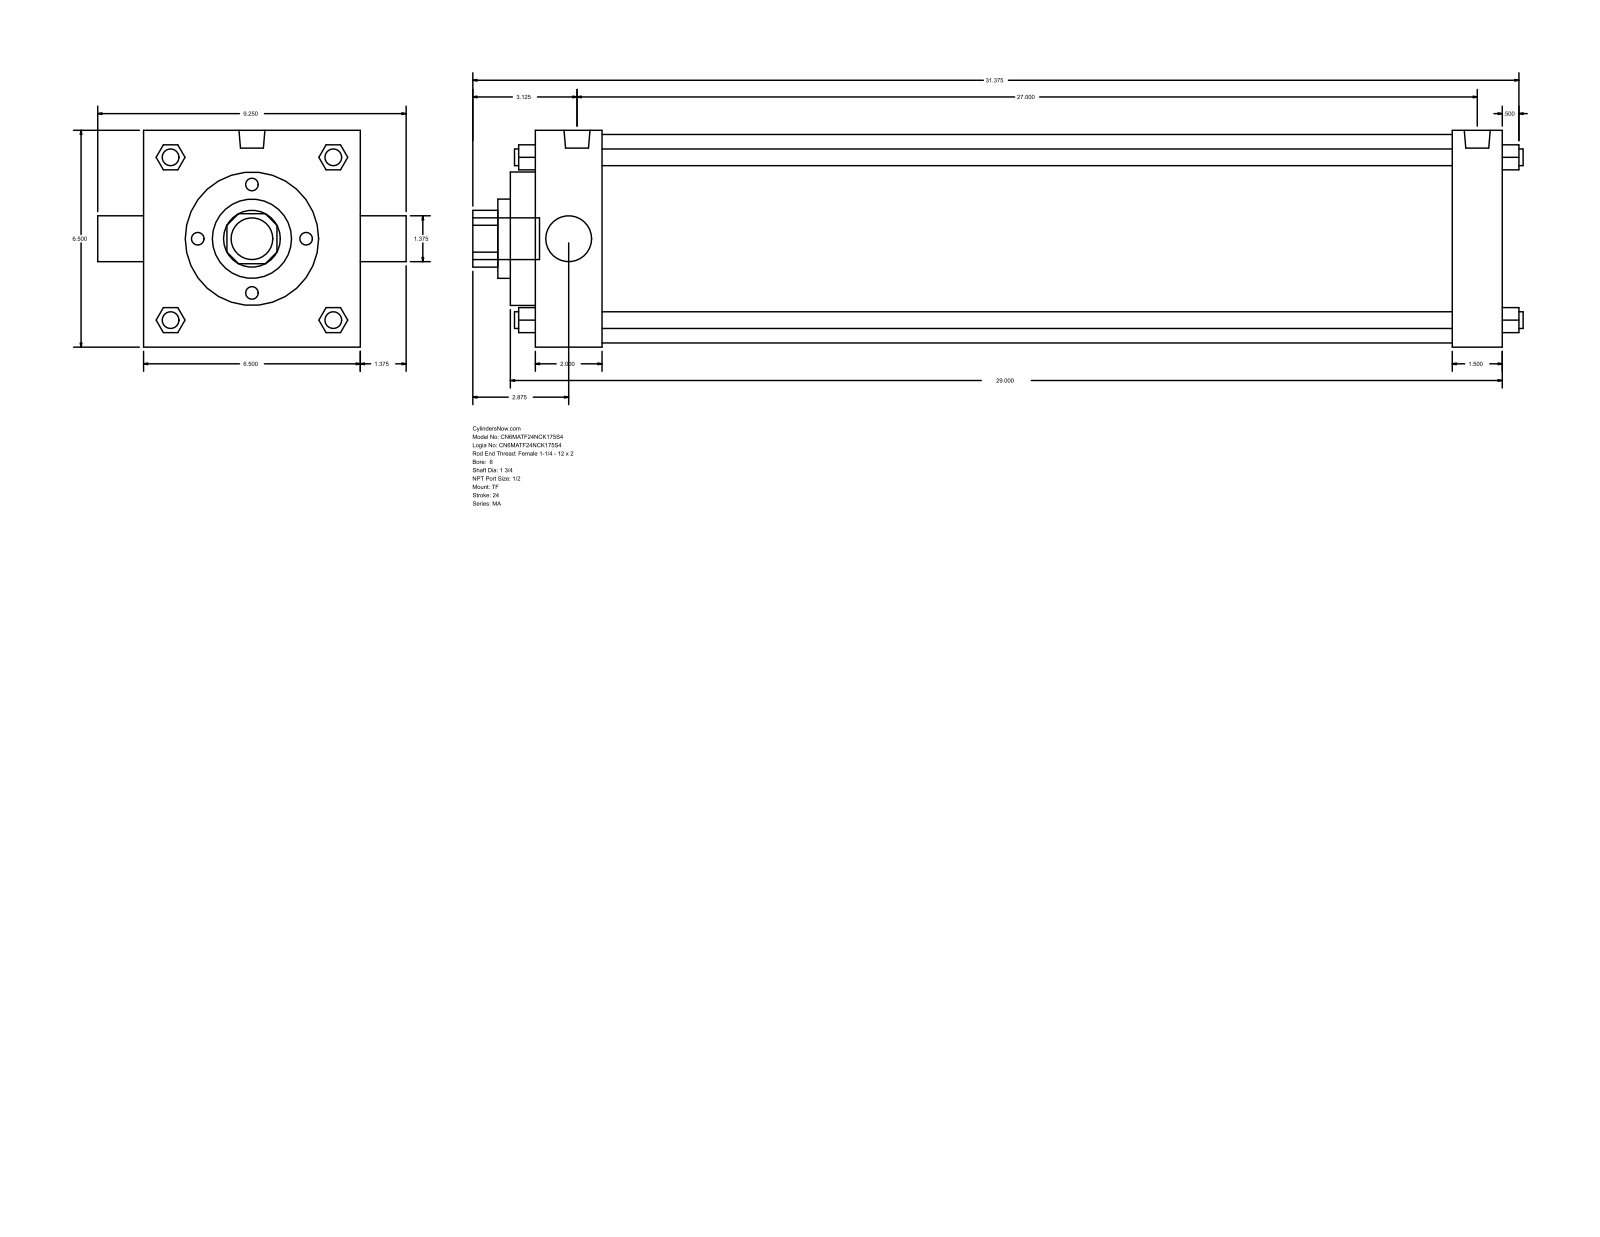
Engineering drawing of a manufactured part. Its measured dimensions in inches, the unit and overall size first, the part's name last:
Units: inches
Overall size (bounding box): 31.5 × 9.25 × 6.5
Round holes (diameter × count): ⌀1.375 ×1, ⌀1.75 ×1, ⌀2.375 ×1, ⌀4 ×1, ⌀6.25 ×1
Round bosses / shafts (diameter × count): ⌀0.5 ×4, ⌀0.687 ×3, ⌀0.778 ×2, ⌀1.25 ×1
Partial cylindrical surfaces — rounded edges, fillets, slot ends (radius × count): R0.852 ×1
Main face-to-face distances: 6.5, 29, 0.75, 2, 27.5, 27, 25.5, 1.5, 2.75, 28.25
Bodies: 0 solids, 122 faces (93 planar, 29 cylindrical, 0 other)
Part name (STEP PRODUCT): MA_TF__0600_1.75
STEP written by: GSSL Pune (CONFIG_CONTROL_DESIGN)
